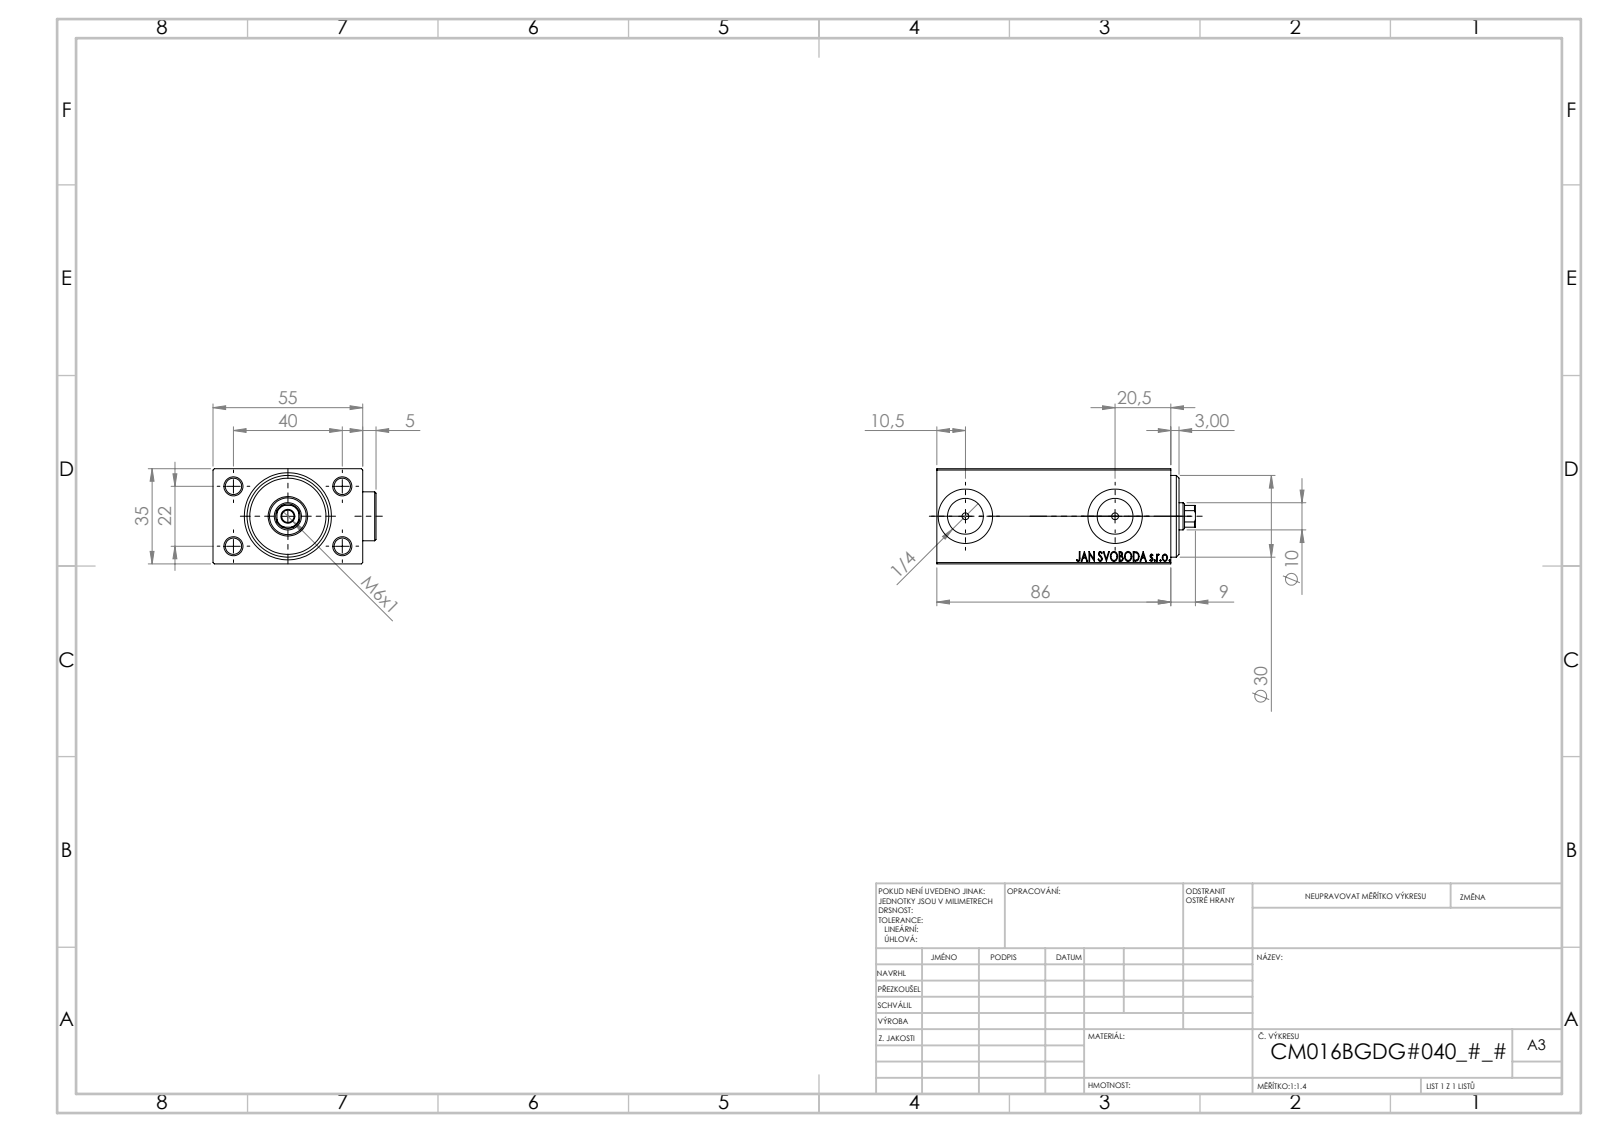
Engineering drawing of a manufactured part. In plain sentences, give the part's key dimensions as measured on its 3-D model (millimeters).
The part is named "V450CM_B_Body; Zatka_OIL_PORT; V450CM_VC_B; V450CM_B_VCP". Its 3-D file was written by "SolidWorks 2019 (CONFIG_CONTROL_DESIGN)". It is 5 solids with 935 faces: 435 planar, 70 cylindrical and 430 other. Overall it measures 95 by 59.9 by 35 millimeters. Its volume is 155 285 cubic millimeters and its surface area 35 688 square millimeters. Round holes: 4 of diameter 6, 2 of diameter 2.5, 2 of diameter 13.16, 2 of diameter 20, 1 of diameter 4.5, 1 of diameter 10, 1 of diameter 13.5, 1 of diameter 14.5, 1 of diameter 16, 1 of diameter 18, 1 of diameter 30. Round bosses or shafts: 2 of diameter 18. Partial cylindrical surfaces (rounded edges, fillets, slot ends): 1 of radius 4.5. The main face-to-face distances are 35, 55, 5, 81, 54.9, 86, 3, 8, 89, 54.8. The hole center spacings are 22.83, 22, 40, 45.65, 55.
